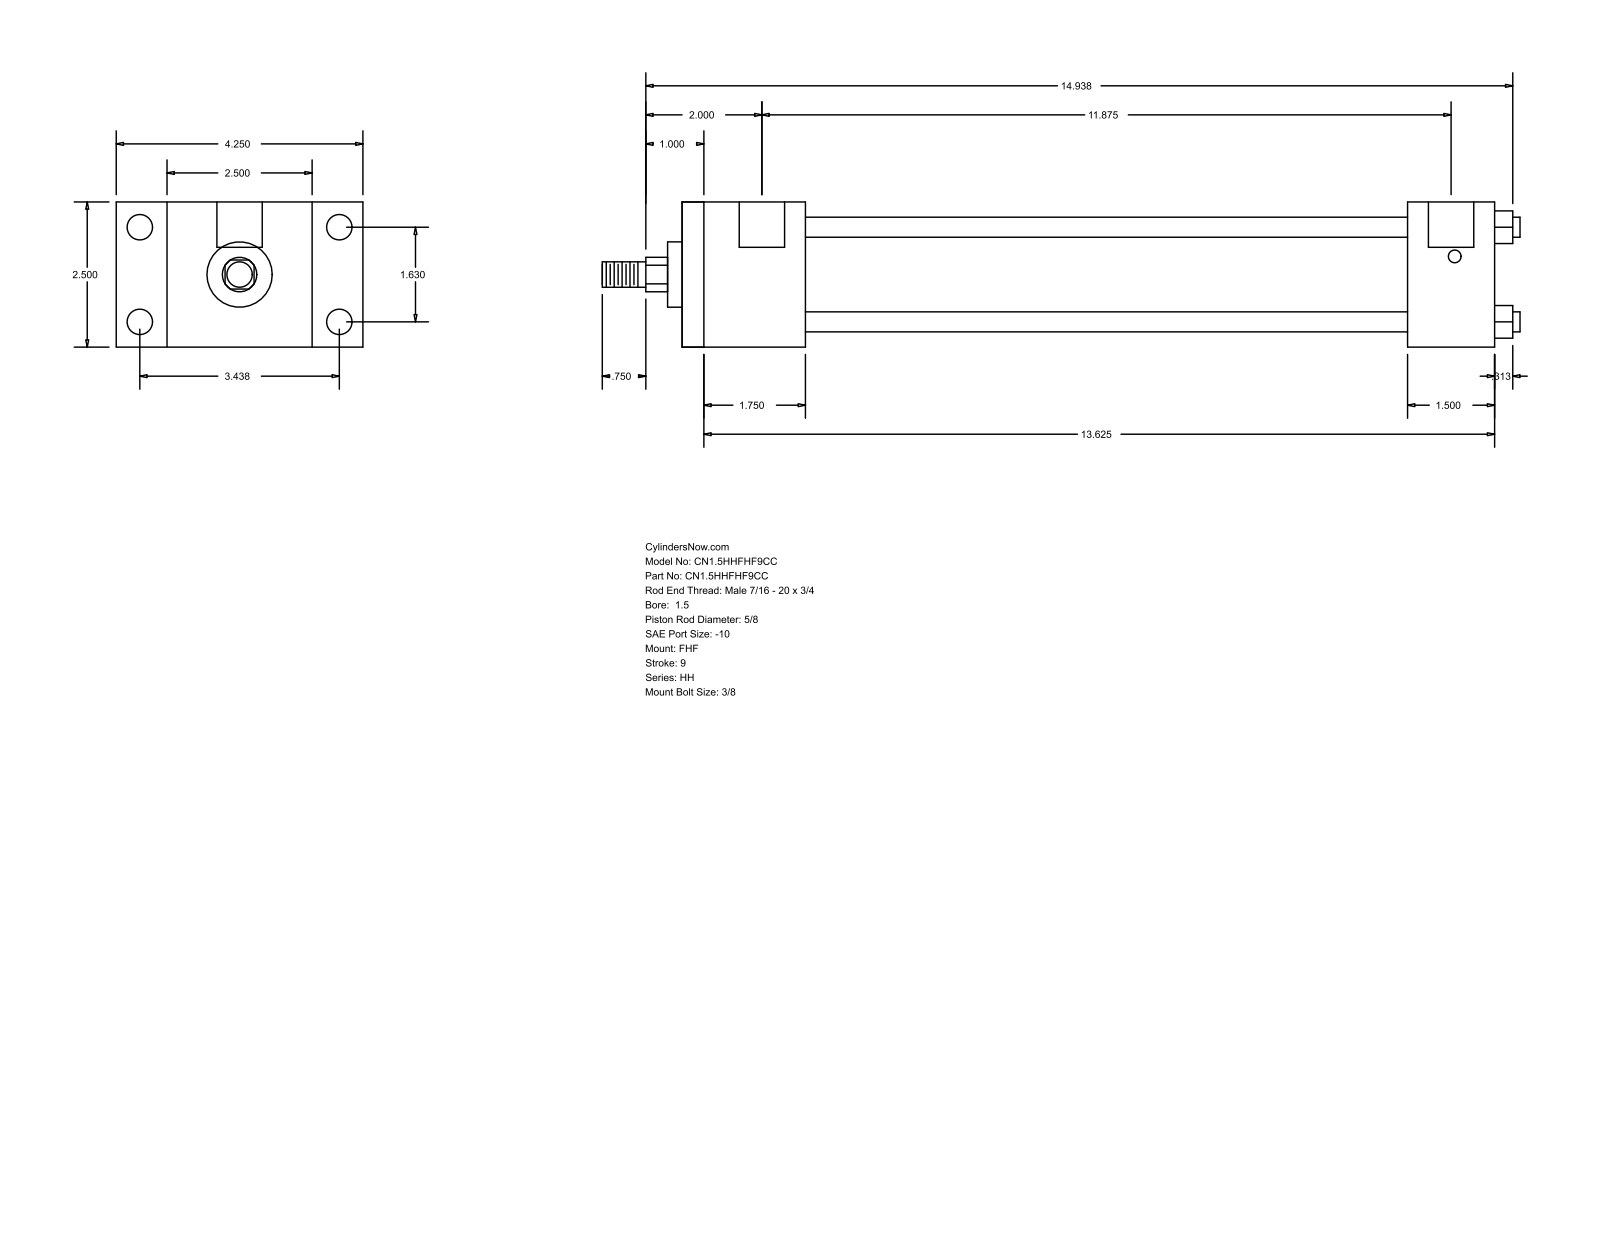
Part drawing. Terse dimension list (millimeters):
name: HH_FHF__0150_0.625
written by: GSSL Pune (CONFIG_CONTROL_DESIGN)
unit: mm
bodies: 0 solids, 88 faces (60 planar, 28 cylindrical, 0 other)
size: 401.64 × 107.95 × 63.5
holes: 4× ⌀5.56, 4× ⌀11.13, 2× ⌀19.84
bosses: 4× ⌀8.76, 1× ⌀44.45, 1× ⌀28.57, 1× ⌀15.88, 1× ⌀11.11
rounds: 1× R7.54
face distances: 63.5, 22.23, 85.73, 53.97, 107.96, 355.6, 301.63, 38.1, 317.5, 263.53
hole spacings: 41.4, 87.32, 96.64, 304.8, 1.58, 1.59, 301.63, 303.21
